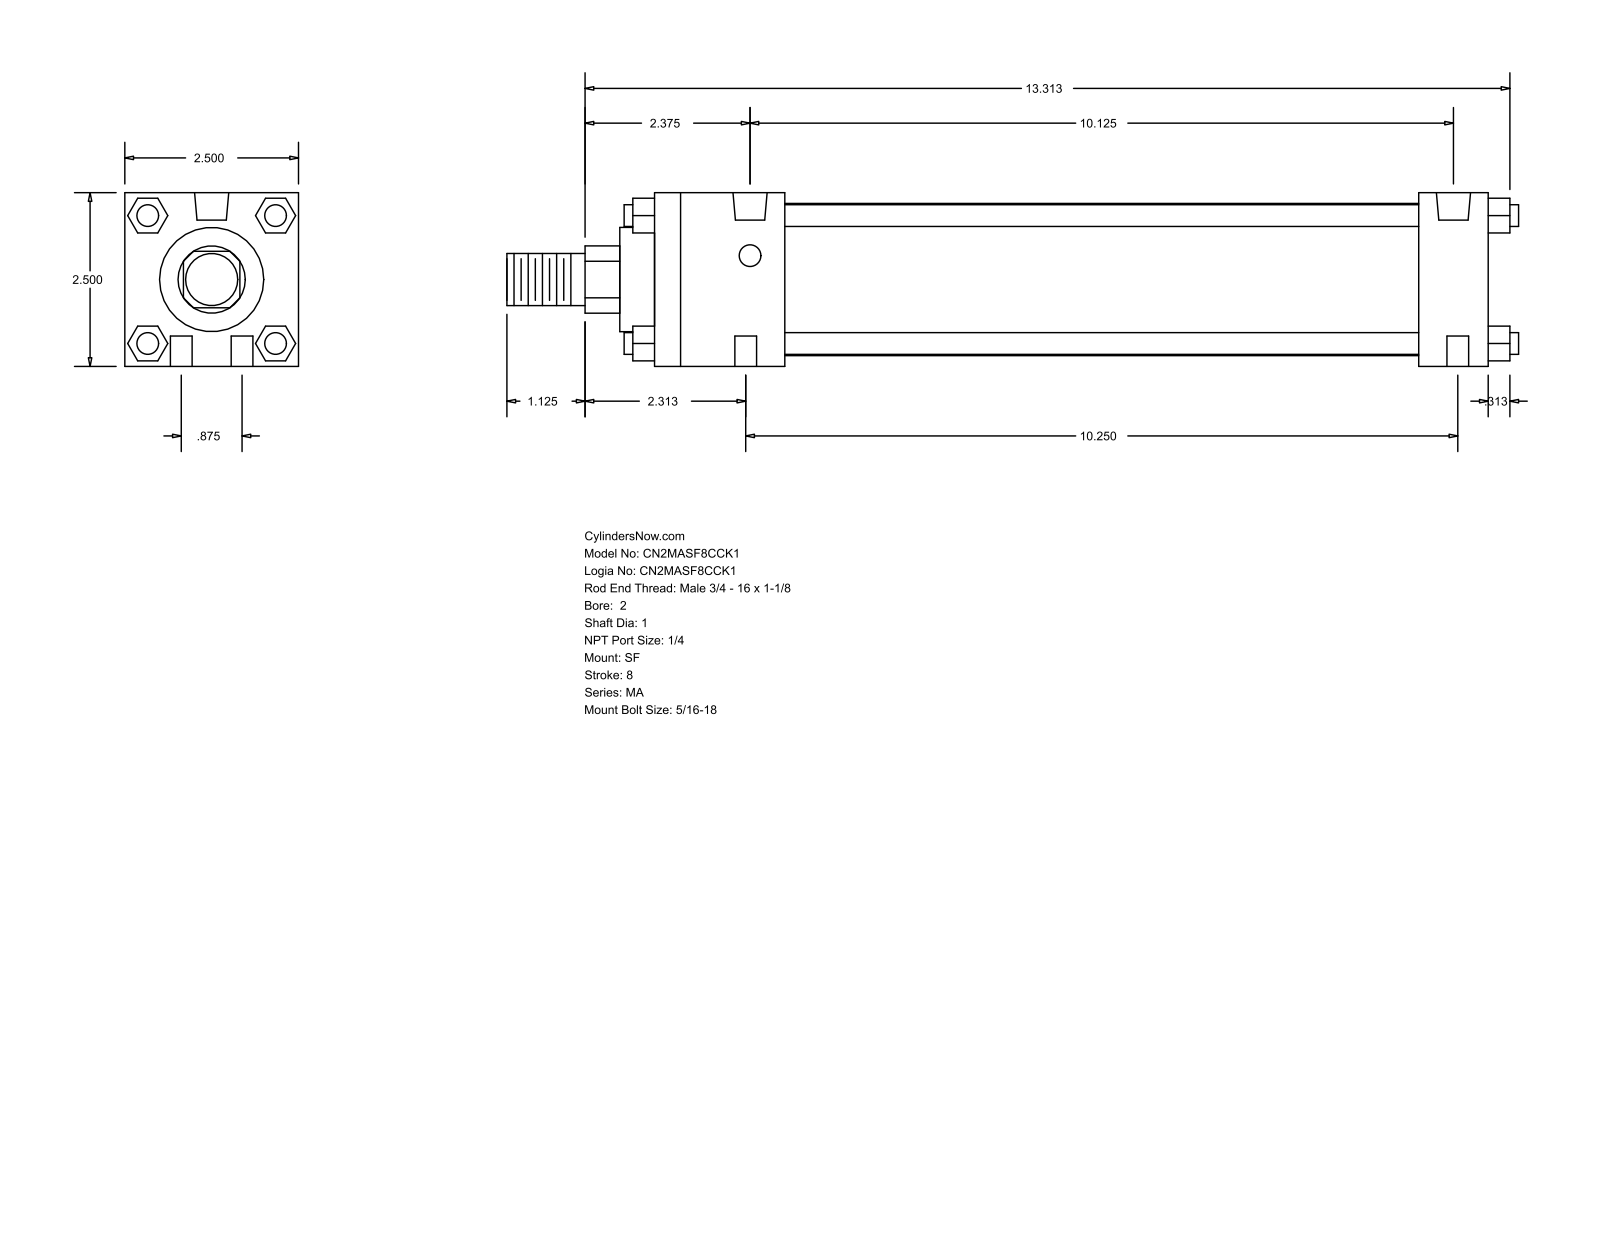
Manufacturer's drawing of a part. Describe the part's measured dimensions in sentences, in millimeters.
The part is named "MA_SF__0200_1". Its 3-D file was written by "GSSL Pune (CONFIG_CONTROL_DESIGN)". It is 0 solids with 124 faces: 94 planar, 30 cylindrical and 0 other. Overall it measures 369.89 by 63.5 by 63.5 millimeters. Round holes: 6 of diameter 7.94, 2 of diameter 12.49. Round bosses or shafts: 4 of diameter 7.94, 1 of diameter 55.63, 1 of diameter 38.1, 1 of diameter 25.4, 1 of diameter 19.05. Partial cylindrical surfaces (rounded edges, fillets, slot ends): 1 of radius 12.29. The main face-to-face distances are 63.5, 304.8, 12.7, 25.4, 279.4, 47.63, 231.77, 257.17, 40.47, 23.37. The hole center spacings are 11.22, 259, 22.22, 257.17, 260.35, 261.3.
